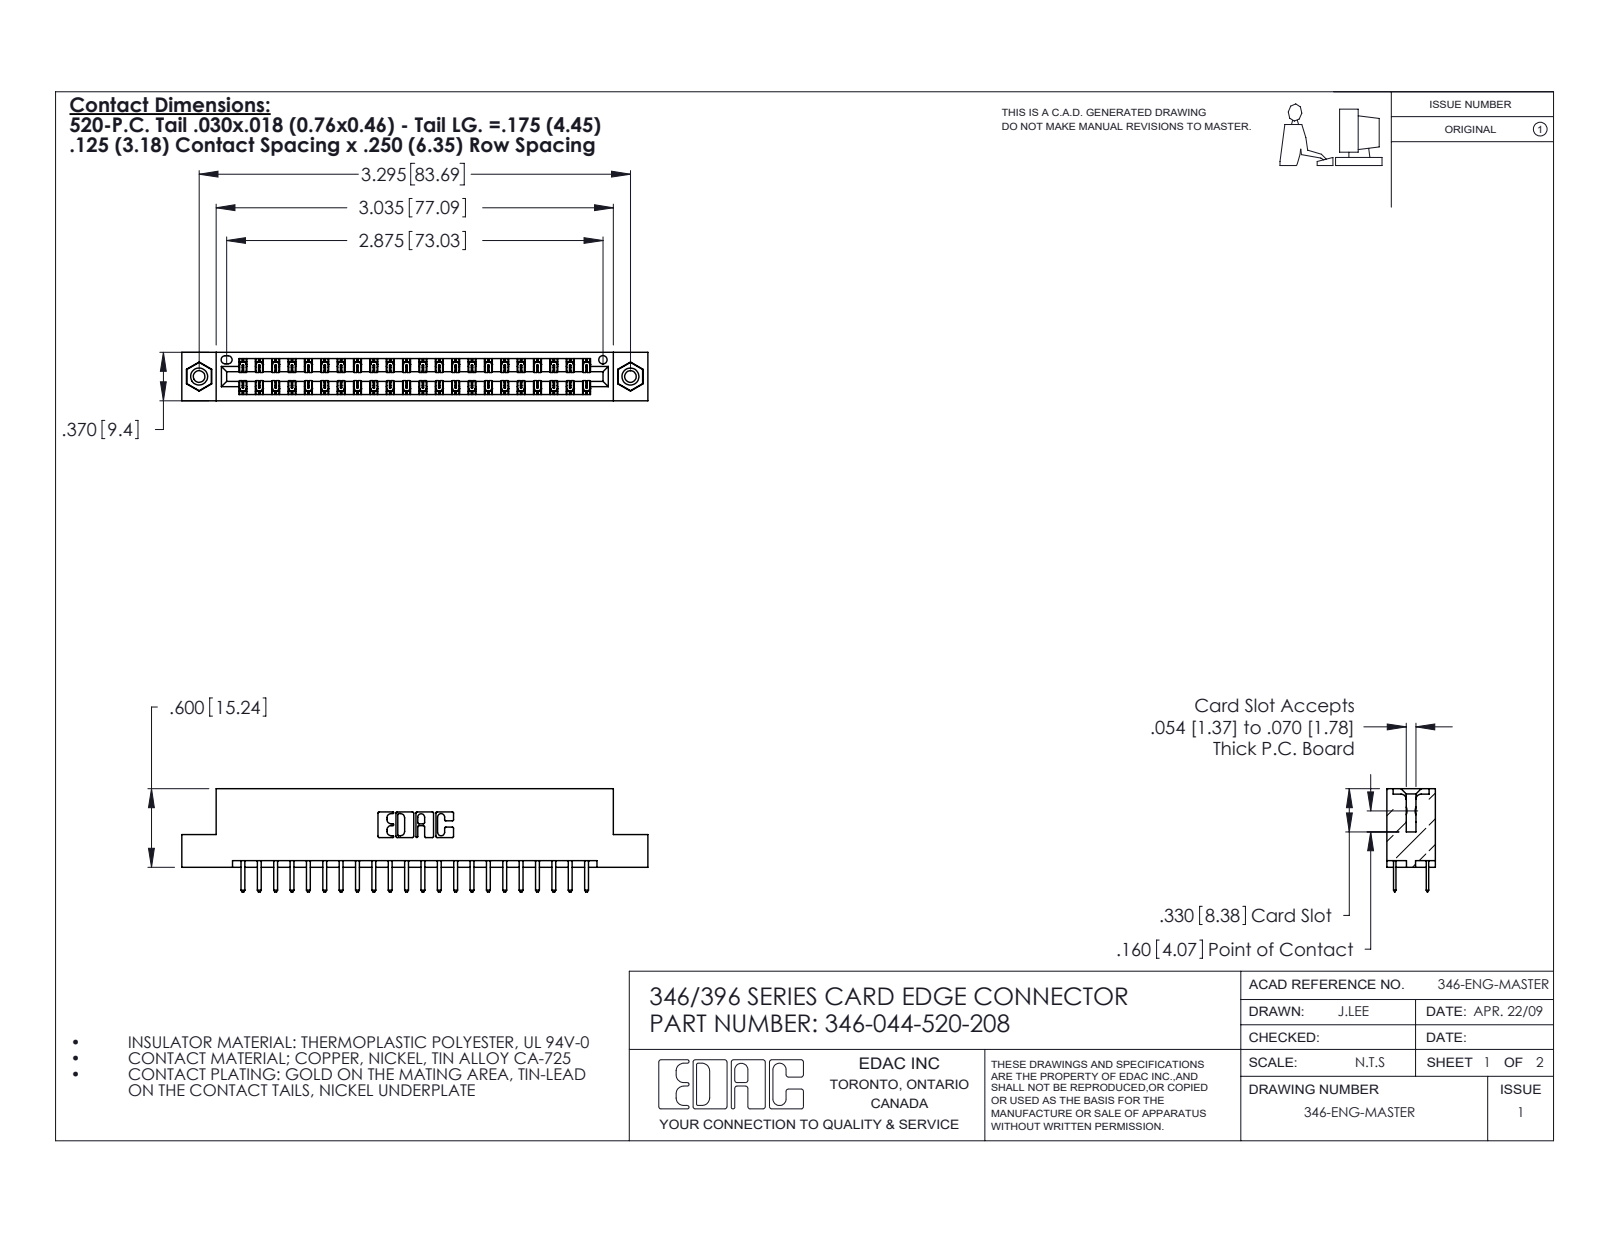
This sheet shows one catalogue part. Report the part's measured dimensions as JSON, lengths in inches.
{"part_name": "346-044-520-208; 346 Part_Flush Mounting Lugs - 0.156 Dia-TI; 345-250-001_345-250-003-102; 345-292-001_345-293-120", "step_written_by": "SolidWorks 2020 (CONFIG_CONTROL_DESIGN)", "units": "inches", "bodies": {"solids": 47, "faces": 2646, "planar": 1736, "cylindrical": 894, "other": 16}, "overall_size": [3.56, 0.788, 0.37], "volume_in3": 0.527, "surface_area_in2": 17.87, "round_holes": [[0.089, 2], [0.125, 2], [0.156, 2], [0.064, 1]], "round_bosses_or_shafts": [[0.155, 2]], "partial_cylinders_radius": [[0.006, 66], [0.01, 48], [0.01, 22], [0.007, 6], [0.031, 6], [0.026, 3], [0.014, 2], [0.022, 2]], "face_to_face_distances": [0.048, 0.322, 0.25, 0.37, 0.275, 0.072, 0.298, 0.025, 0.148, 0.222], "hole_center_spacings": [0.246, 3.087, 3.295]}
